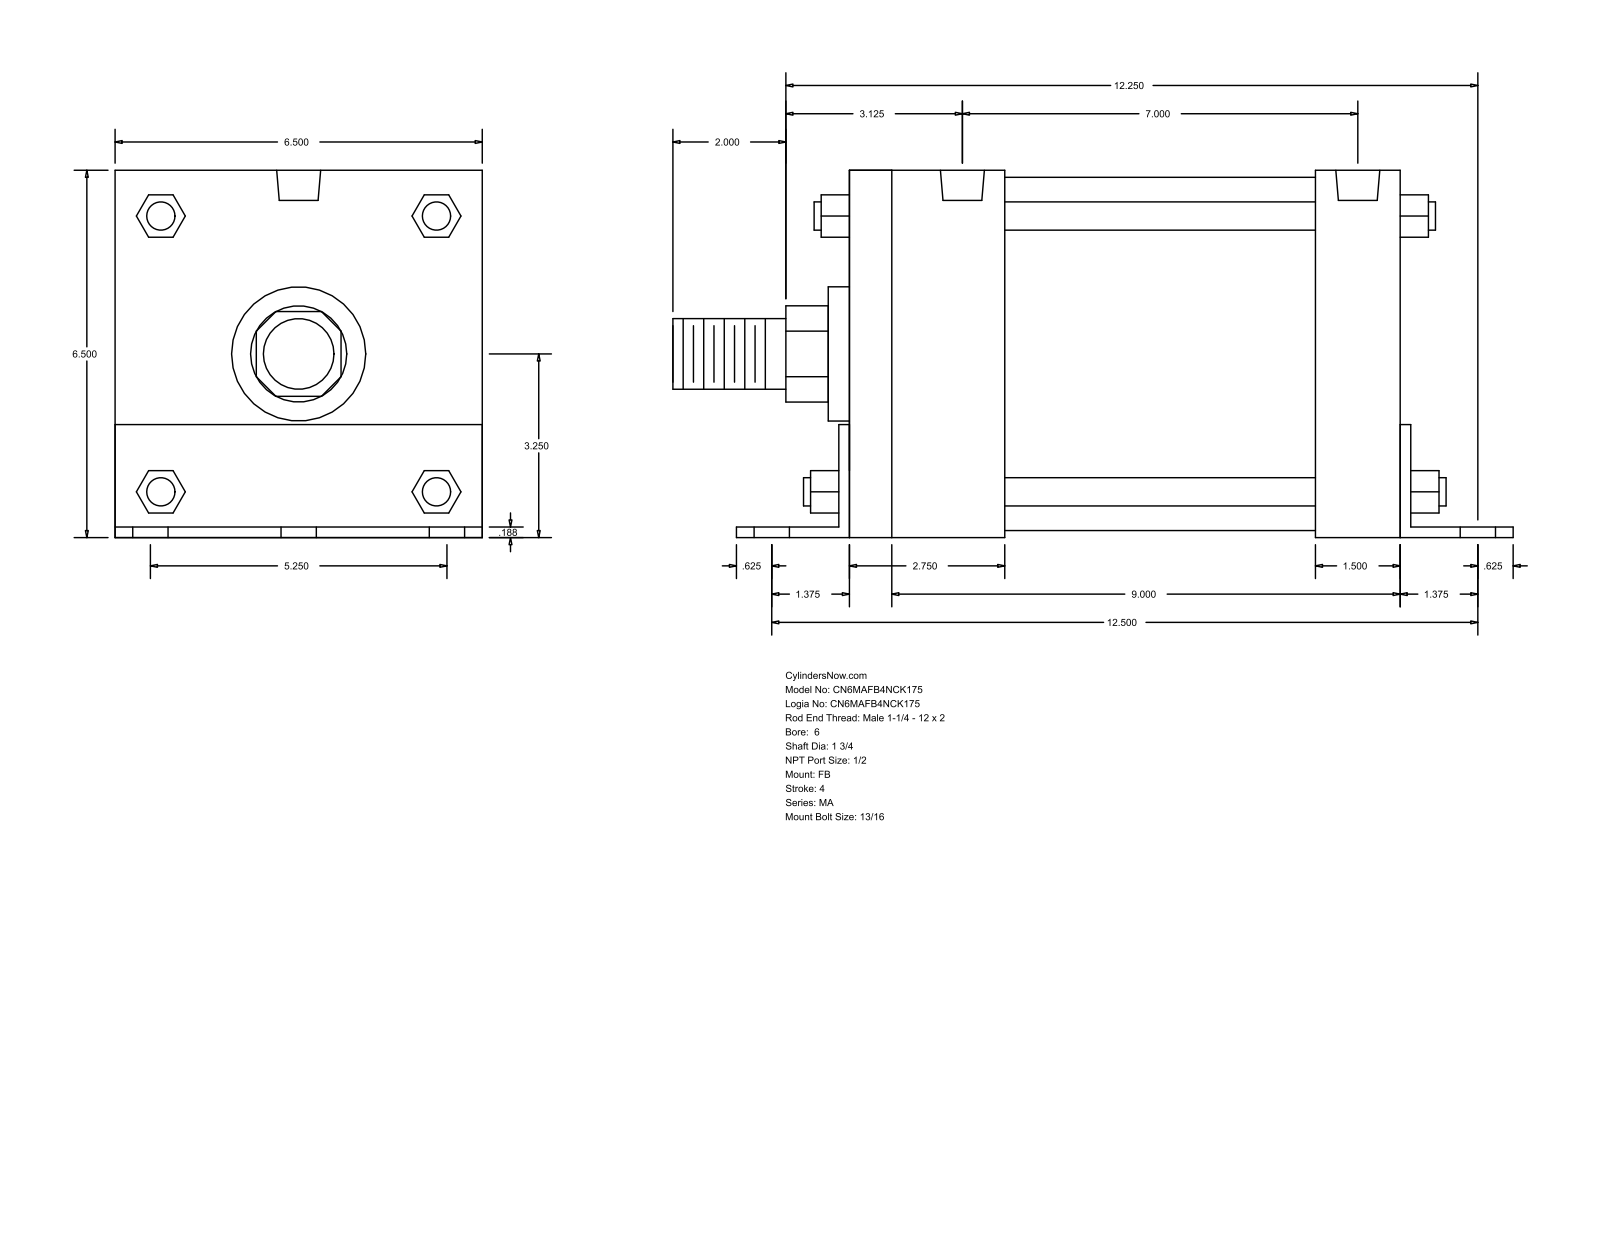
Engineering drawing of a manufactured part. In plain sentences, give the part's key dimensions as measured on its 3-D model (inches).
The part is named "MA_FB__0600_1.75". Its 3-D file was written by "GSSL Pune (CONFIG_CONTROL_DESIGN)". It is 0 solids with 140 faces: 105 planar, 35 cylindrical and 0 other. Overall it measures 14.875 by 6.502 by 6.5 inches. Round holes: 6 of diameter 0.813, 4 of diameter 0.687, 2 of diameter 0.778. Round bosses or shafts: 4 of diameter 0.5, 1 of diameter 6.25, 1 of diameter 2.375, 1 of diameter 1.75, 1 of diameter 1.25. Partial cylindrical surfaces (rounded edges, fillets, slot ends): 1 of radius 0.852, 1 of radius 1.262. The main face-to-face distances are 6.5, 0.187, 9.75, 6.502, 9.938, 0.185, 6.315, 10.125, 2.75, 2.937. The hole center spacings are 2.625, 12.772, 12.5, 3.377, 4.276, 5.25, 7, 9.495.
